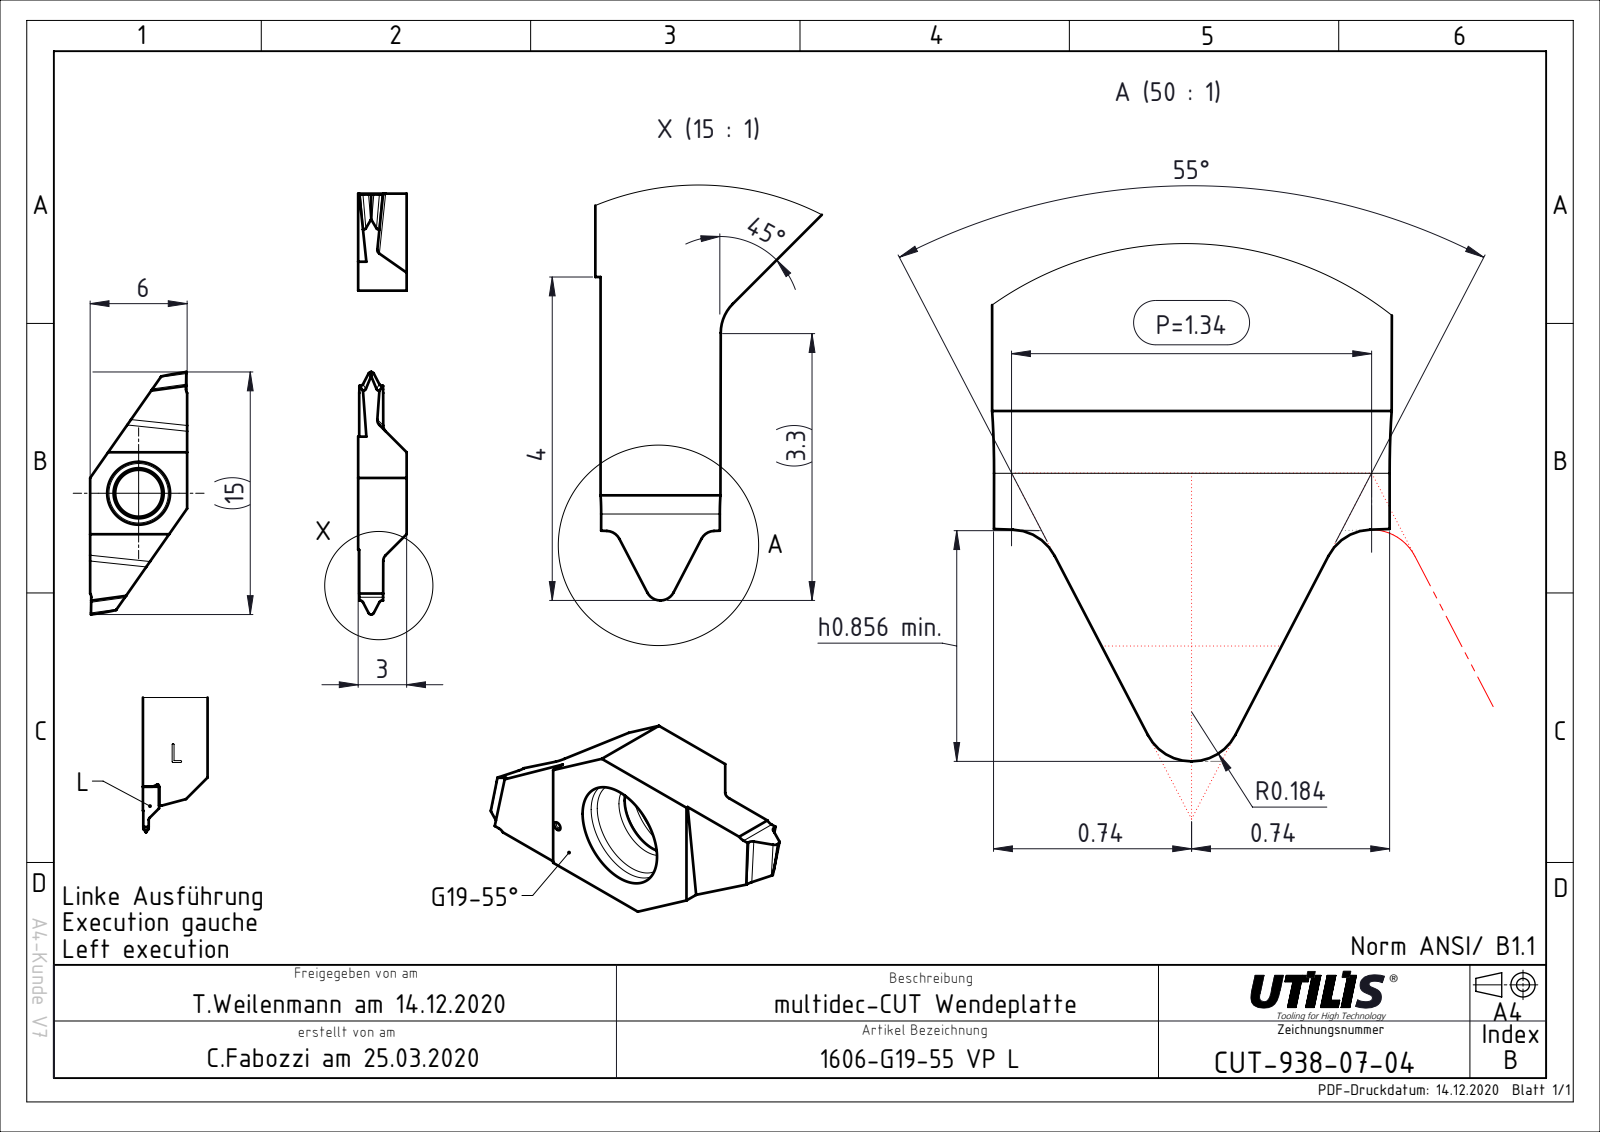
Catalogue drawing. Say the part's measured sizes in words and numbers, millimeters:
The part is named "CUT-938-07; ASME Y14.5". Its 3-D file was written by "FormatWorks Professional (AP242_MANAGED_MODEL_BASED_3D_ENGINEERING_MIM_LF)". It is 1 solid with 42 faces: 24 planar, 14 cylindrical and 4 other. Overall it measures 15 by 6 by 3 millimeters. Its volume is 119 cubic millimeters and its surface area 209 square millimeters. Round holes: 1 of diameter 2.9. Partial cylindrical surfaces (rounded edges, fillets, slot ends): 8 of radius 0.18, 2 of radius 0.4, 2 of radius 0.5. The main face-to-face distances are 6, 3, 81.1, 3.2, 9.2, 12.4, 7, 11.75, 11.76.
